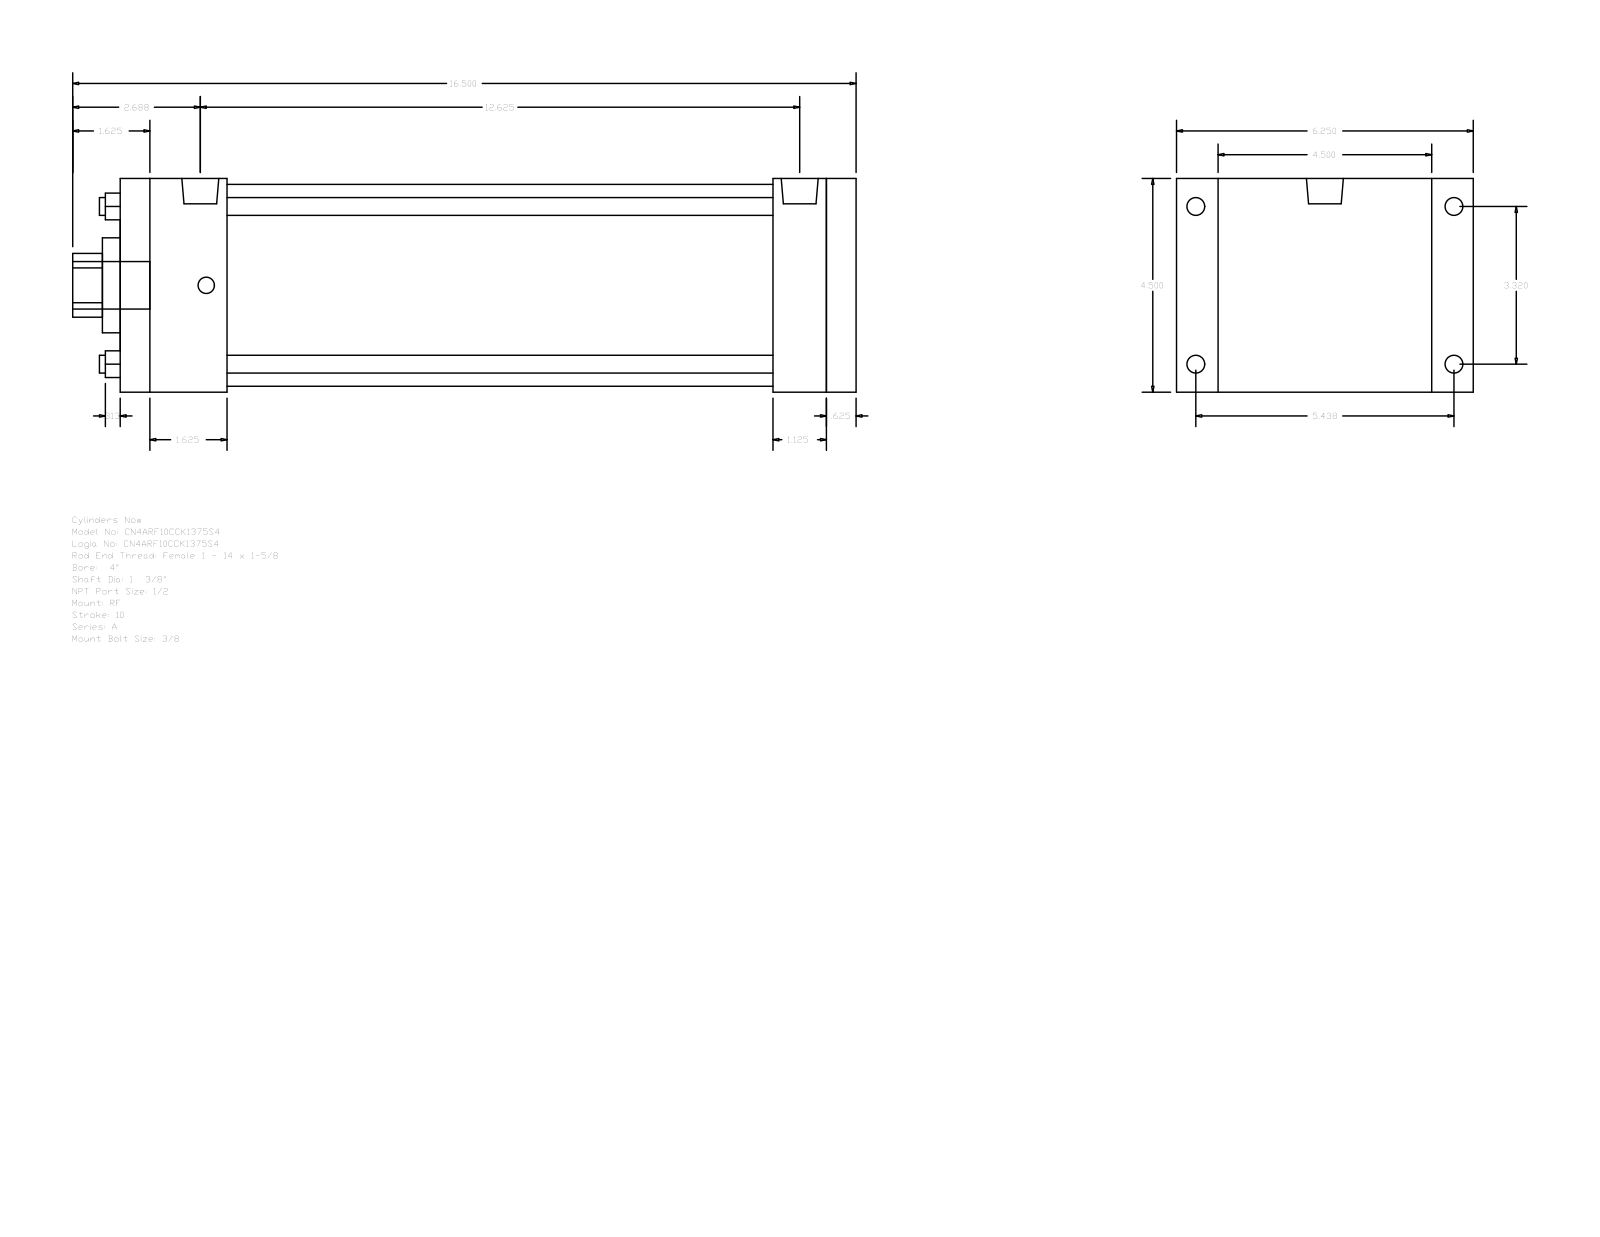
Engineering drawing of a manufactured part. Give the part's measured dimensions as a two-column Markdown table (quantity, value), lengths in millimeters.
| quantity | value |
| --- | --- |
| part name | A_RF__0400_1.375 |
| STEP written by | GSSL Pune (CONFIG_CONTROL_DESIGN) |
| units | millimeters |
| bodies | 0 solids, 92 faces (64 planar, 28 cylindrical, 0 other) |
| overall size | 419.1 × 158.75 × 114.3 |
| round holes (diameter × count) | 9.53 × 4, 34.92 × 1, 50.8 × 1, 107.95 × 1 |
| round bosses / shafts (diameter × count) | 9.53 × 4, 8.73 × 4, 19.77 × 2, 25.4 × 1 |
| partial cylindrical surfaces (radius × count) | 17.06 × 1 |
| main face-to-face distances | 114.3, 393.7, 15.87, 377.83, 28.58, 22.23, 136.53, 349.25, 44.45, 57.15 |
| hole center spacings | 59.62, 84.32, 119.25 |
